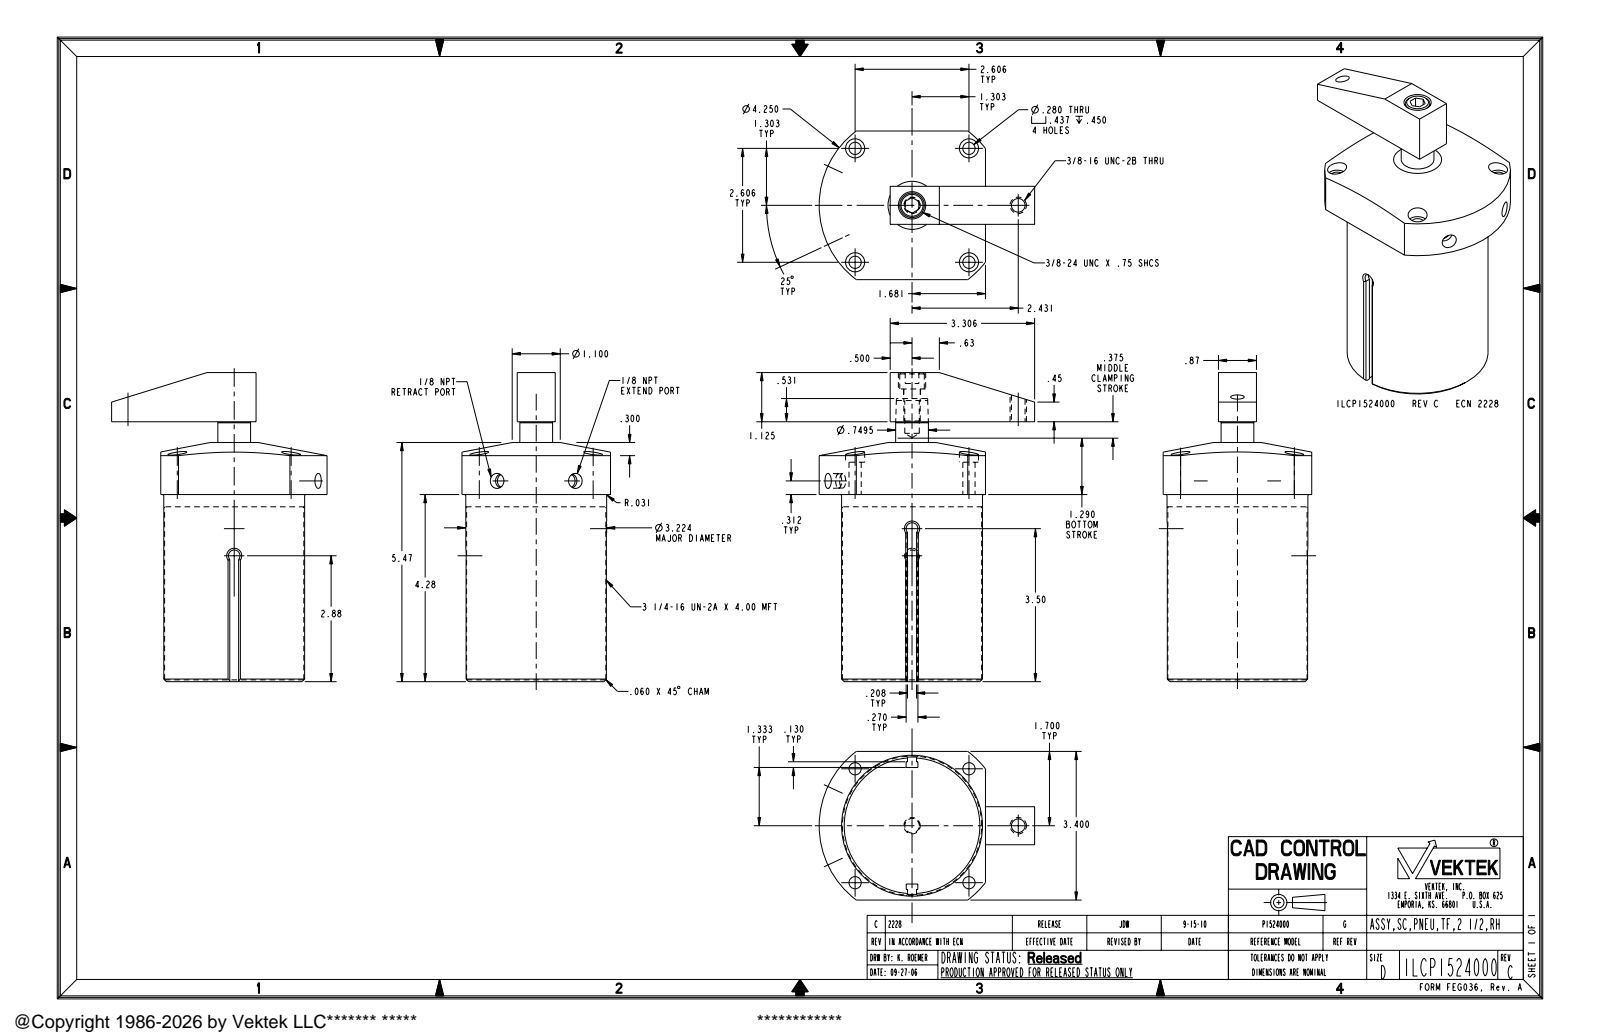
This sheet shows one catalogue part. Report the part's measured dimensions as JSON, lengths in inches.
{"part_name": "ILCP1524000; ILC91502503; ILCP1524000_ASM", "step_written_by": "PRO/ENGINEER BY PARAMETRIC TECHNOLOGY CORPORATION, 2007460 (AUTOMOTIVE_DESIGN_CC2)", "units": "inches", "bodies": {"solids": 2, "faces": 123, "planar": 52, "cylindrical": 47, "other": 24}, "overall_size": [7.07, 4.931, 3.4], "volume_in3": 49.17, "surface_area_in2": 148, "round_holes": [[0.28, 4], [0.437, 4], [0.328, 2], [0.312, 1], [0.332, 1], [0.39, 1], [0.625, 1]], "round_bosses_or_shafts": [[0.375, 2], [3.224, 1], [3.187, 1], [0.75, 1], [0.562, 1]], "partial_cylinders_radius": [[0.132, 1], [0.135, 1], [2.125, 1]], "face_to_face_distances": [1.265, 2.135, 4.28, 0.87, 3.4, 1.665, 5.945, 0.367, 3.033, 0.898], "hole_center_spacings": [1.843, 2.606, 1.724, 3.685, 3.955, 2.431]}
